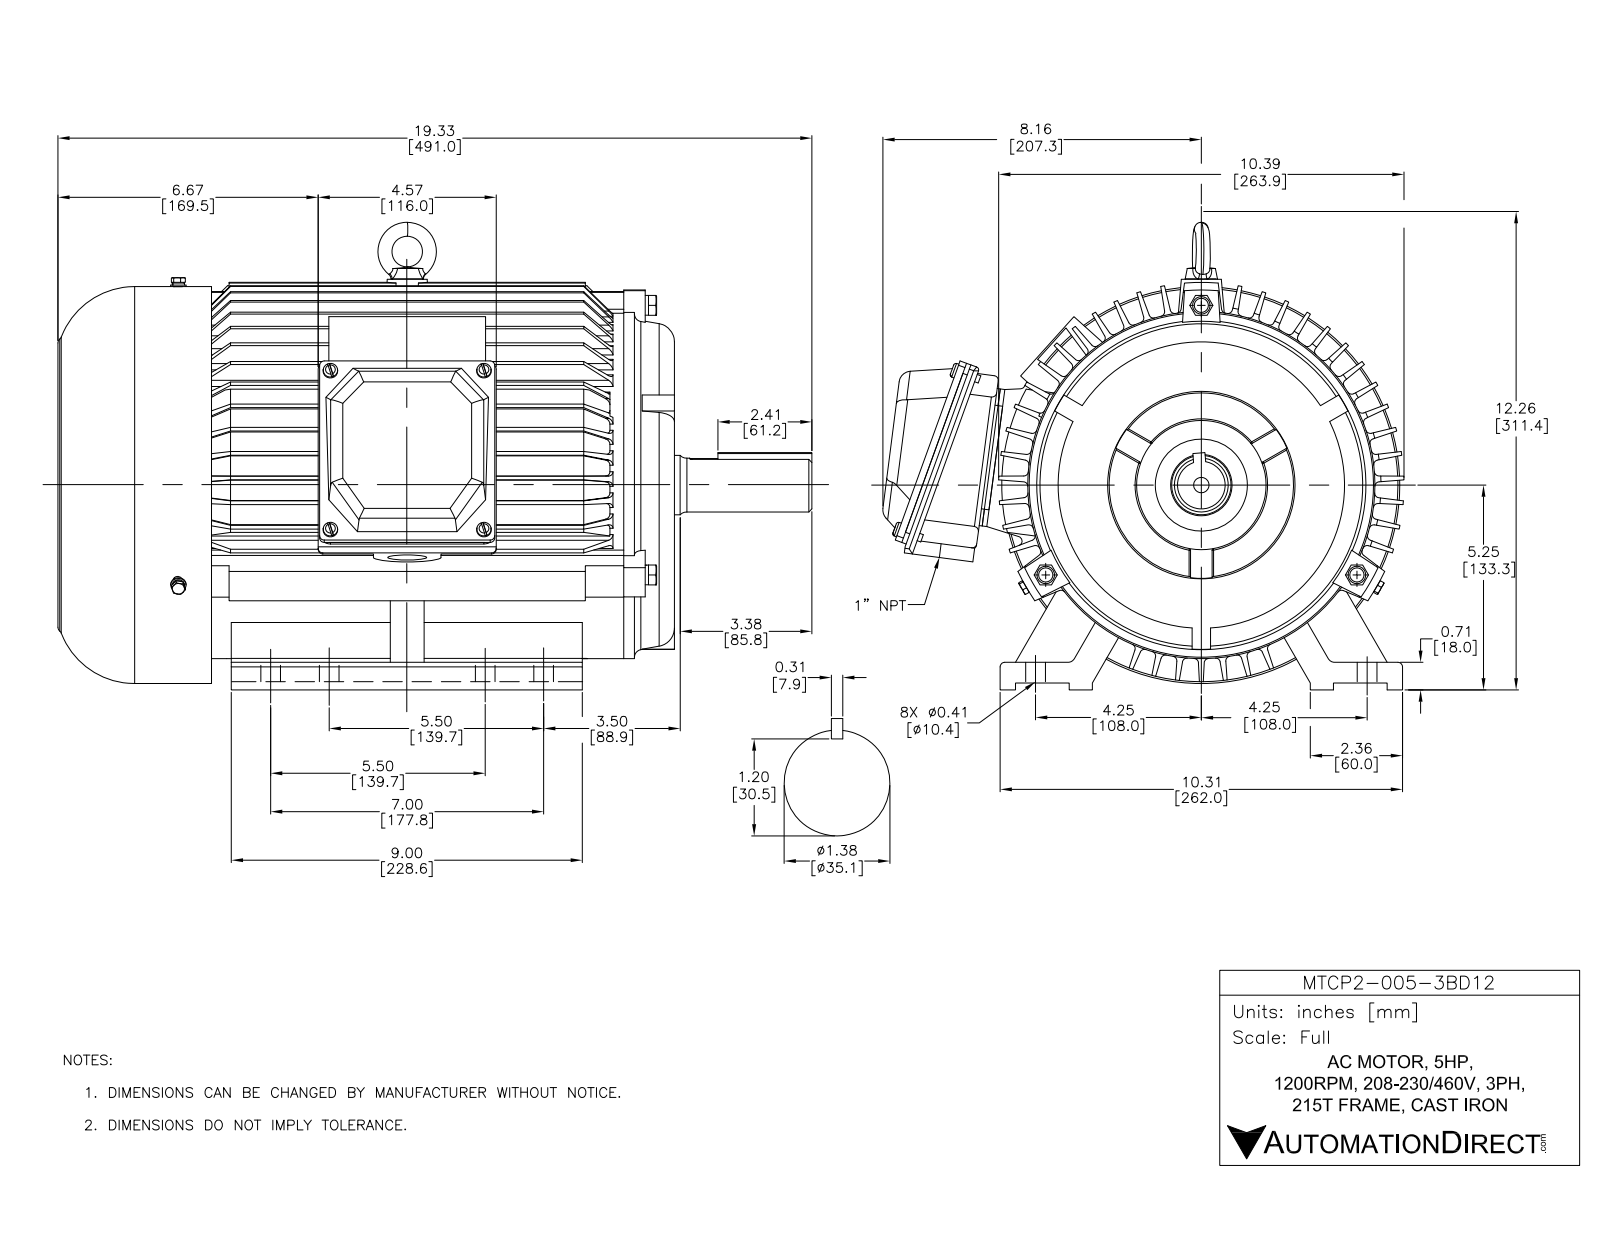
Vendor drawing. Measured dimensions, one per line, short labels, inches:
name: MTCP2-005-3BD12 215T
written by: SolidWorks 2017 (AUTOMOTIVE_DESIGN)
unit: in
bodies: 27 solids, 1887 faces (1094 planar, 527 cylindrical, 266 other)
size: 19.331 × 13.36 × 11.986
volume: 259.5 in³; area: 2 071 in²
holes: 8× ⌀0.228, 8× ⌀0.433, 6× ⌀0.197, 4× ⌀0.165, 4× ⌀0.236, 4× ⌀0.276, 3× ⌀0.209, 3× ⌀0.213, 3× ⌀0.315, 3× ⌀0.342, 3× ⌀0.362, 3× ⌀0.394
bosses: 7× ⌀0.197, 4× ⌀0.315, 3× ⌀0.507, 3× ⌀0.394, 3× ⌀0.283, 1× ⌀10.173, 1× ⌀10.079, 1× ⌀8.898
rounds: 104× R0.118, 17× R0.276, 12× R0.039, 8× R0.059, 8× R0.157, 8× R0.315, 6× R0.091, 6× R0.433
face distances: 0.709, 0.157, 15.699, 0.177, 0.531, 0.047, 15.746, 0.236, 15.463, 15.51
hole spacings: 3.937, 5.853, 4.331, 2.677, 1.5, 2.678, 3.785, 3.786
